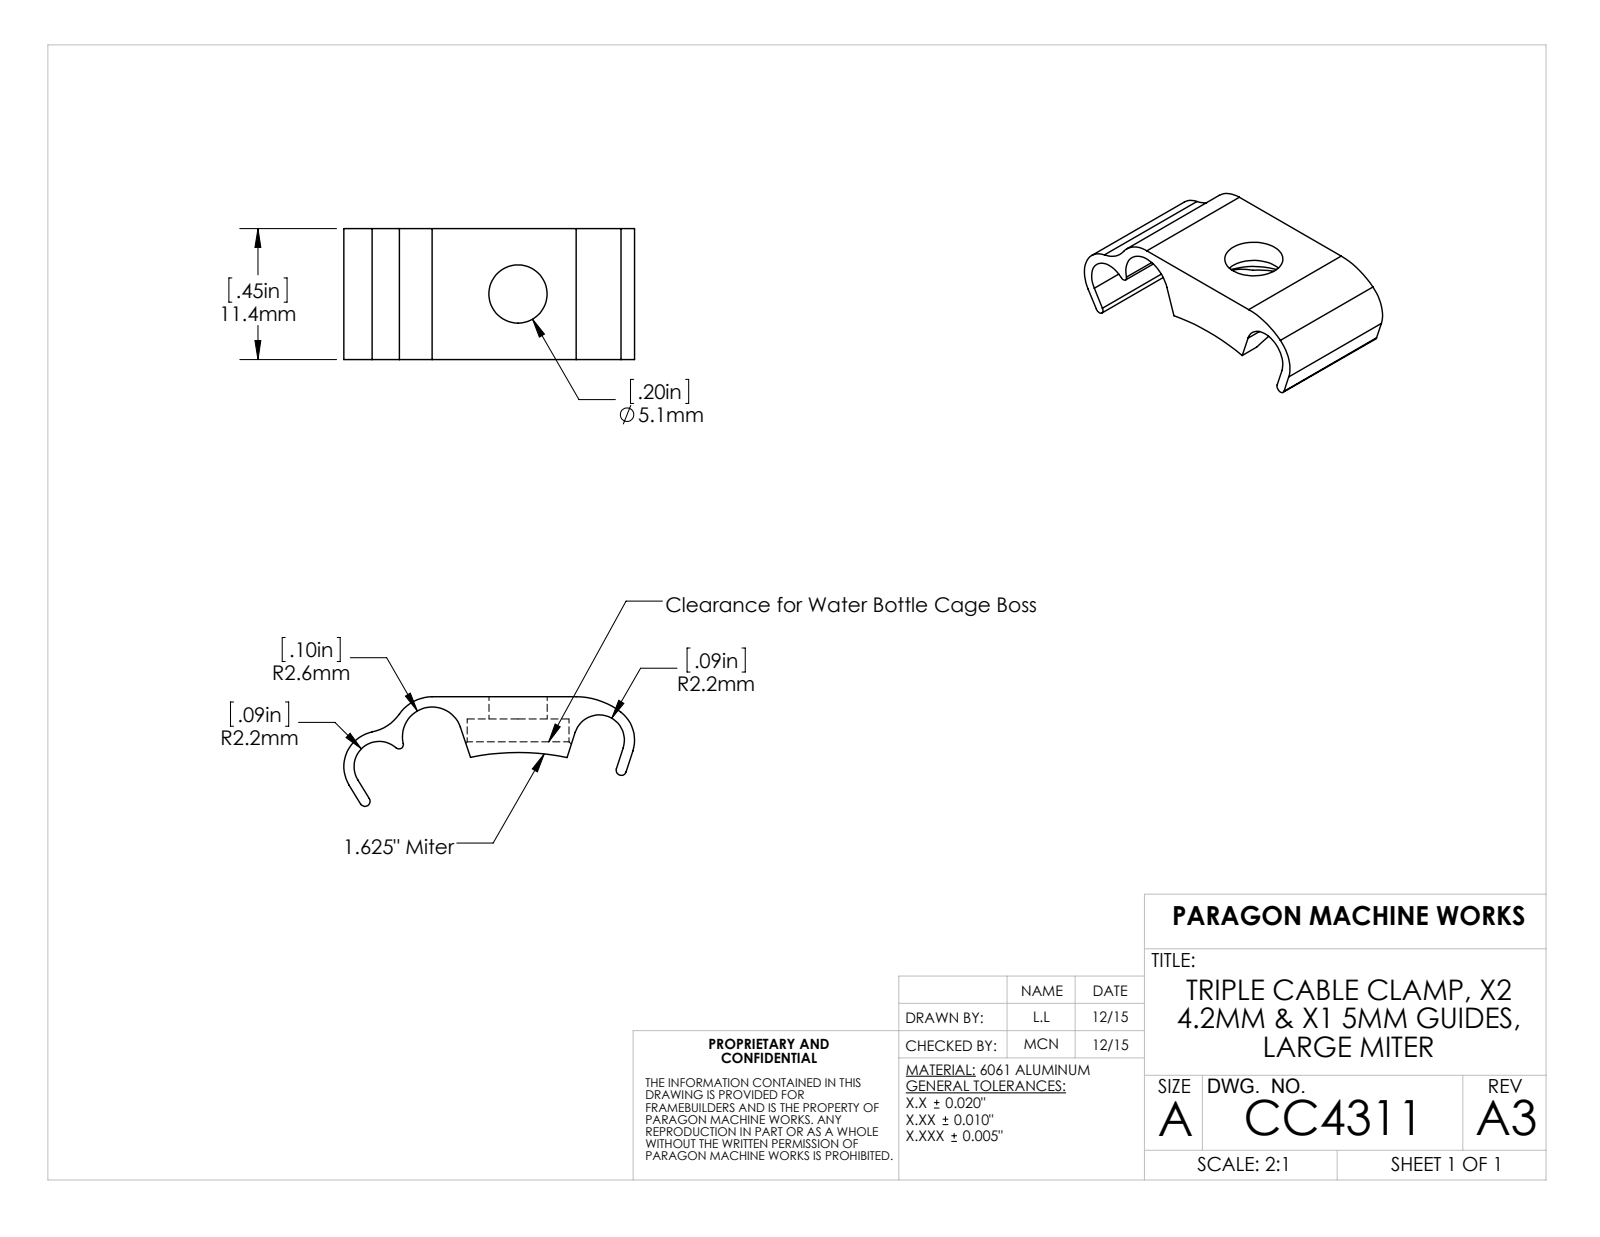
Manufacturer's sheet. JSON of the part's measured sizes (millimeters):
{"part_name": "CC4311", "step_written_by": "SolidWorks 2015 (AUTOMOTIVE_DESIGN)", "units": "millimeters", "bodies": {"solids": 1, "faces": 33, "planar": 10, "cylindrical": 21, "other": 2}, "overall_size": [25.4, 11.4, 9.6], "volume_mm3": 640, "surface_area_mm2": 1102, "round_holes": [[5.1, 1], [8.9, 1]], "partial_cylinders_radius": [[0.5, 2], [2.2, 2], [3.1, 2], [0.4, 1], [2.6, 1], [3.5, 1], [3.8, 1], [6.4, 1]], "face_to_face_distances": [11.4, 0.9, 1.9, 4.4, 5.3]}
